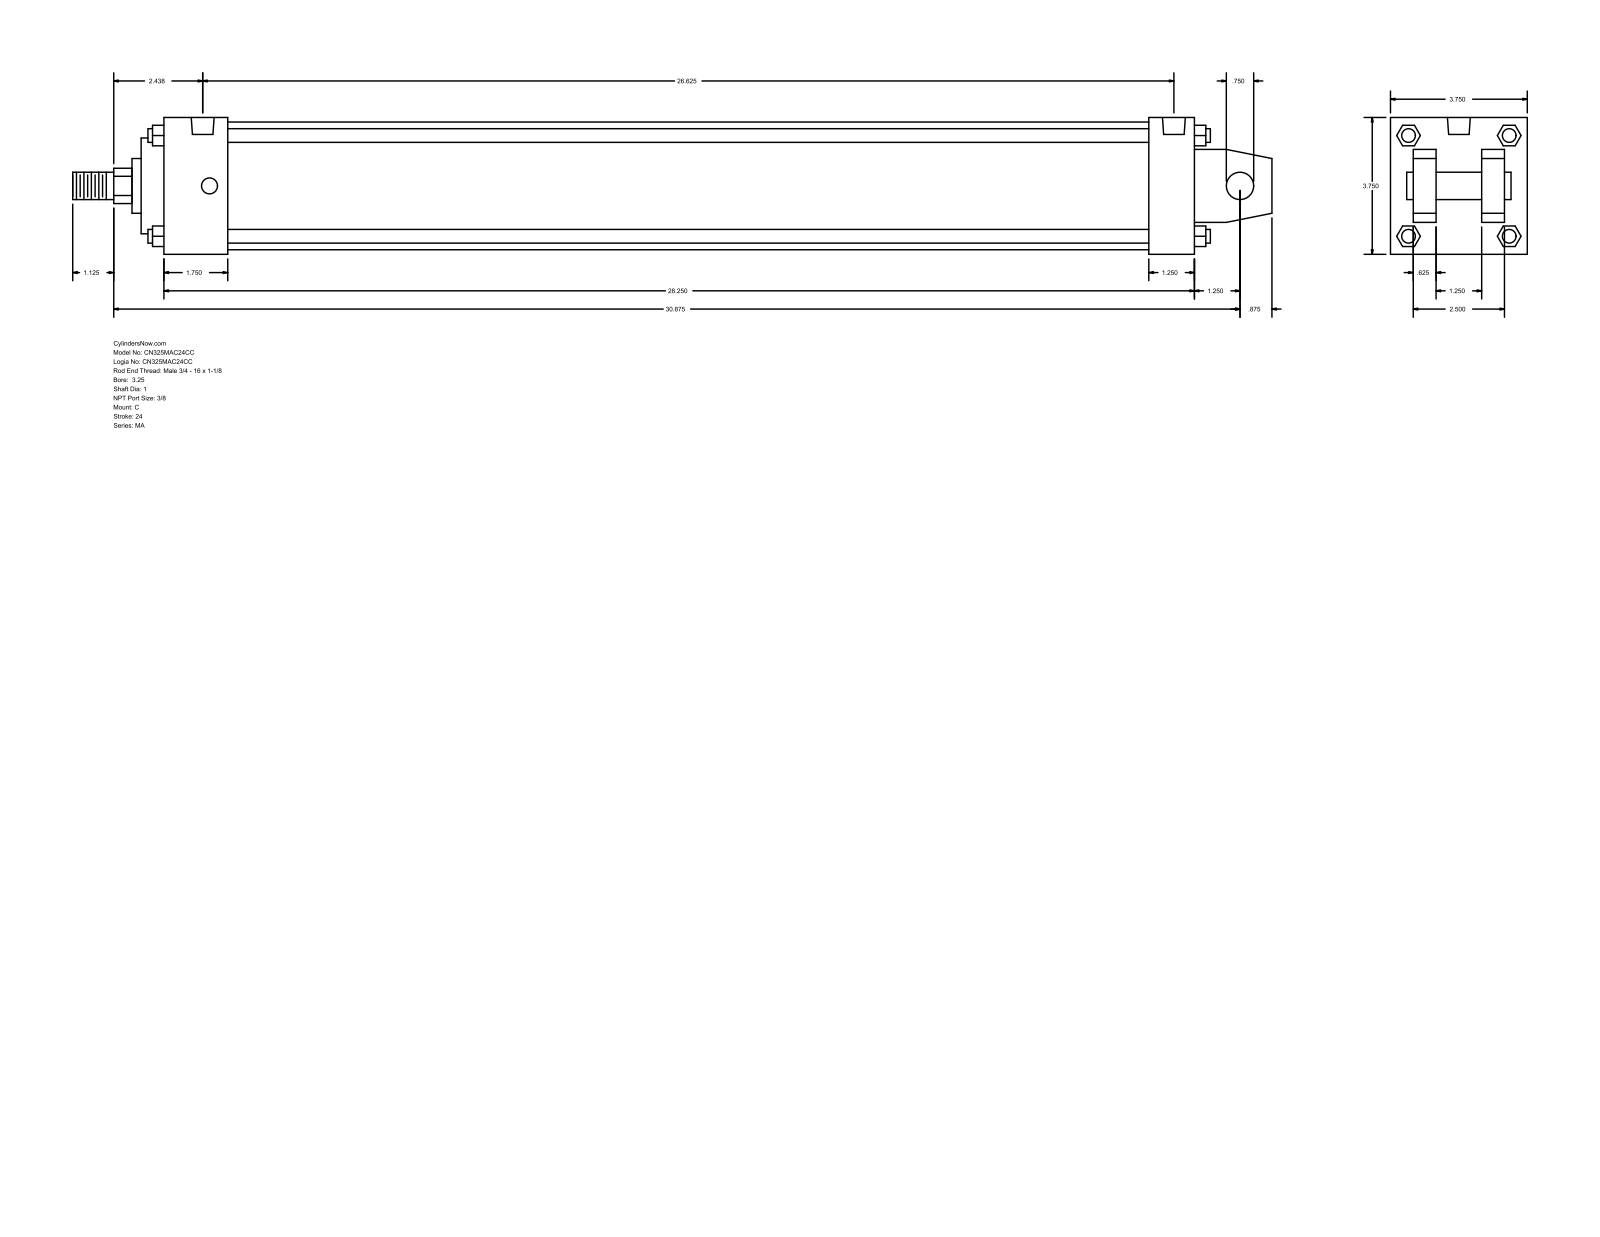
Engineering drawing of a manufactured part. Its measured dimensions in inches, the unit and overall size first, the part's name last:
Units: inches
Overall size (bounding box): 32.875 × 3.75 × 3.75
Round holes (diameter × count): ⌀0.437 ×4, ⌀0.627 ×2
Round bosses / shafts (diameter × count): ⌀0.375 ×4, ⌀0.75 ×2, ⌀3.5 ×1, ⌀2.625 ×1, ⌀1.5 ×1, ⌀1 ×1
Partial cylindrical surfaces — rounded edges, fillets, slot ends (radius × count): R0.484 ×1
Main face-to-face distances: 3.75, 0.625, 2.5, 28.25, 1.25, 3.125, 1.875, 27, 1.25, 1.75
Hole centre spacings: 26.25, 0.187, 0.188, 26.437, 26.438, 26.625
Bodies: 0 solids, 141 faces (109 planar, 32 cylindrical, 0 other)
Part name (STEP PRODUCT): MA_C__0325_1
STEP written by: GSSL Pune (CONFIG_CONTROL_DESIGN)
